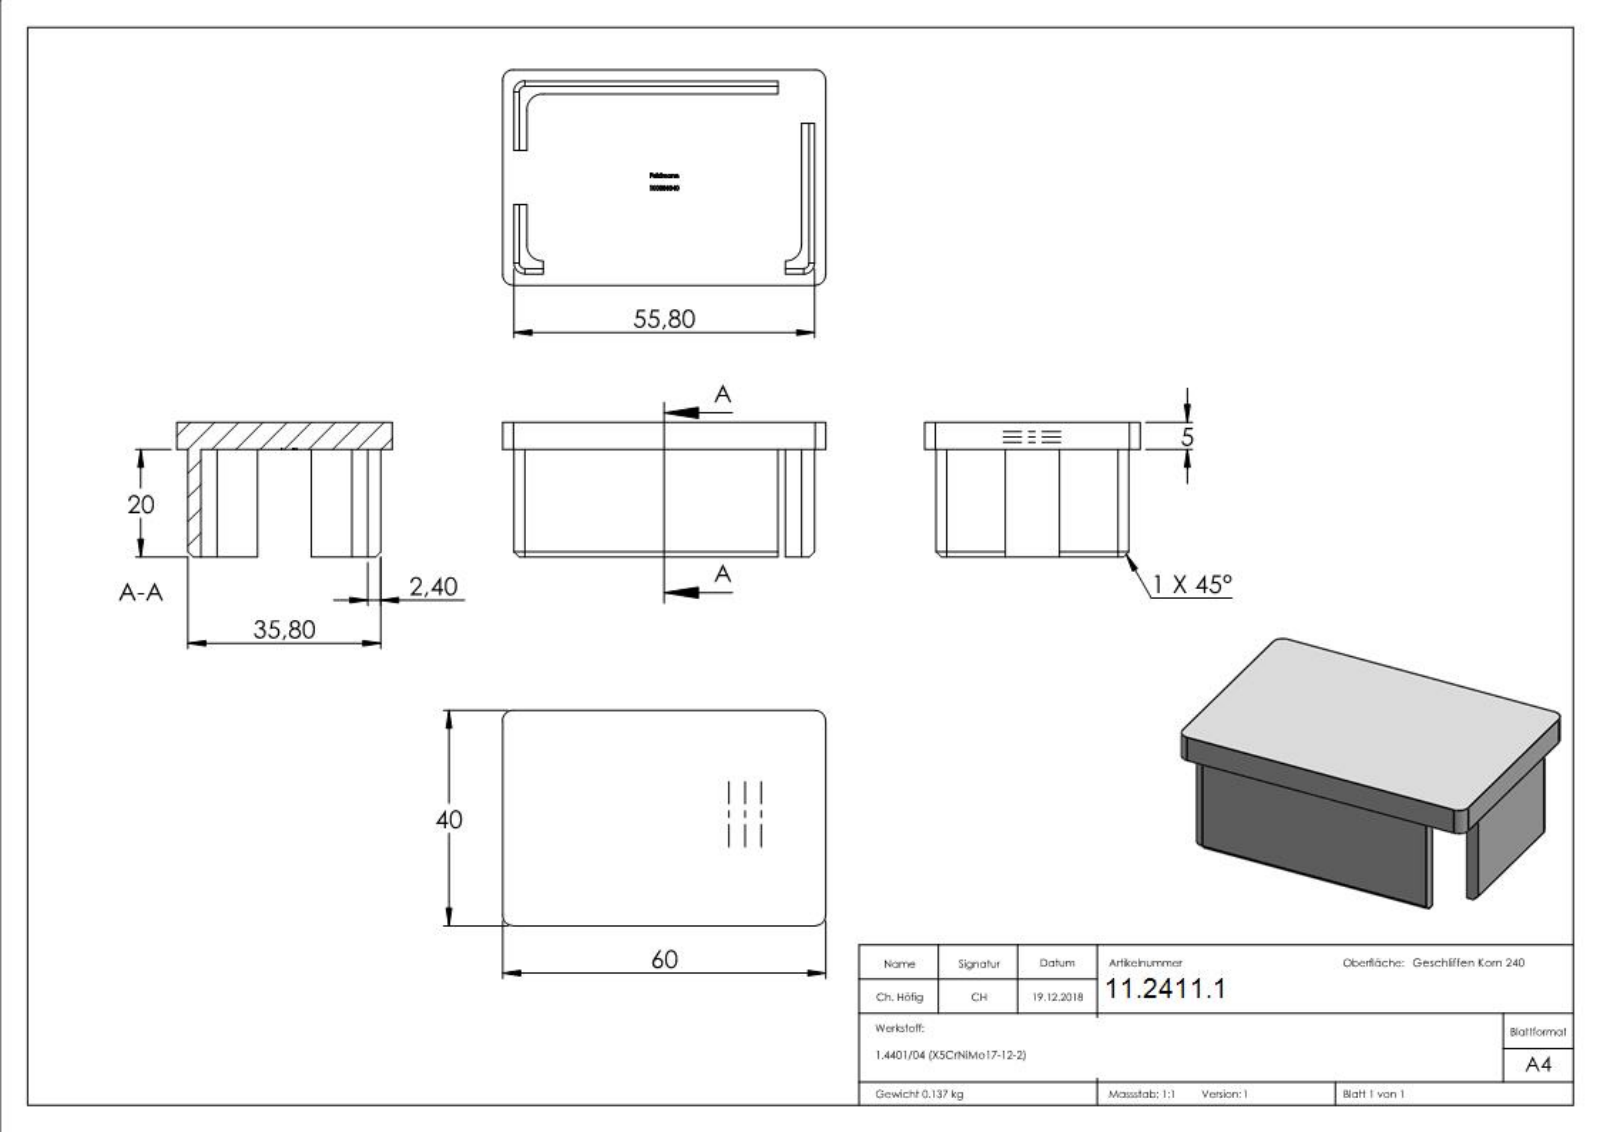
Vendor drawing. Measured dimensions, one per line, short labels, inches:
name: 100036040
written by: SolidWorks 2015 (CONFIG_CONTROL_DESIGN)
unit: in
bodies: 1 solid, 266 faces (137 planar, 10 cylindrical, 119 other)
size: 2.362 × 1.575 × 0.984
volume: 1.043 in³; area: 15.7 in²
rounds: 7× R0.079, 3× R0.118
face distances: 0.197, 0.094, 0.083, 2.102, 0.177, 2.197, 1.492, 2.185, 2.28, 2.008
